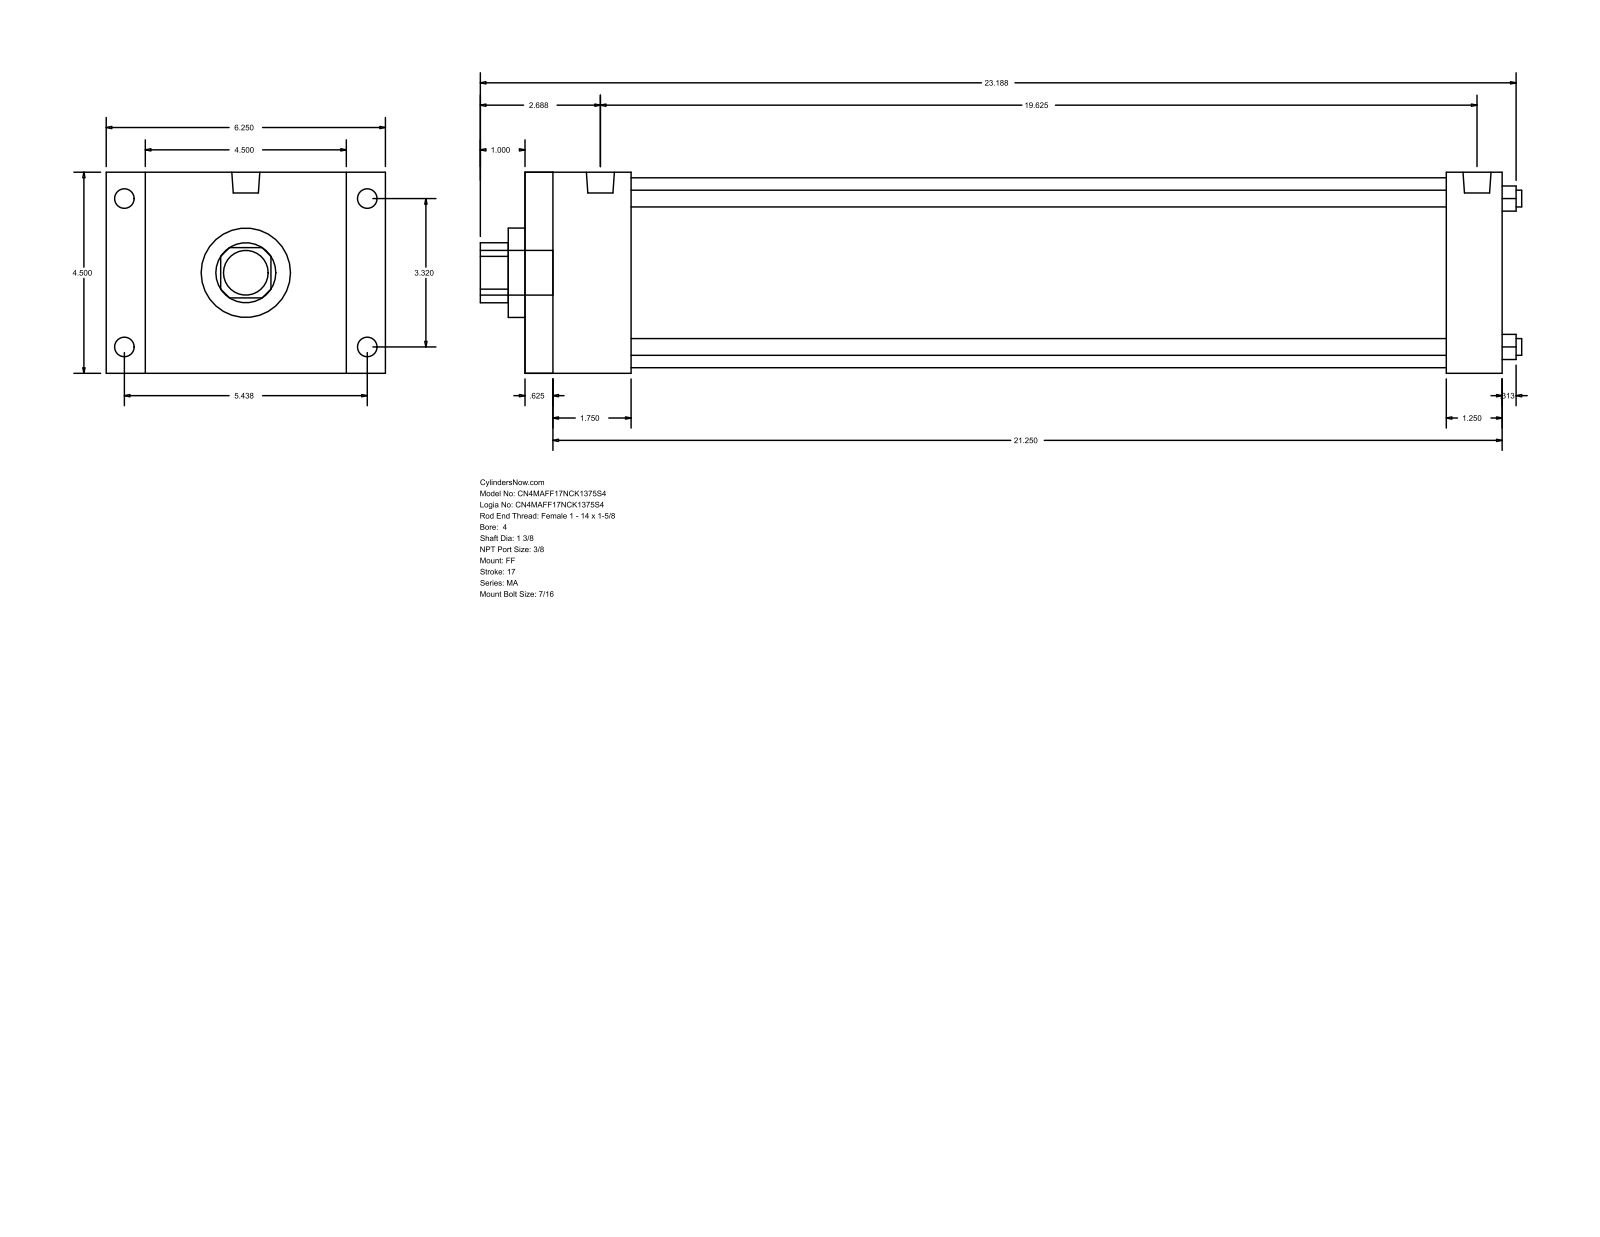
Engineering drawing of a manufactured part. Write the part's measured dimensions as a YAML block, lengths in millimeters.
part_name: "MA_FF__0400_1.375"
step_written_by: "GSSL Pune (CONFIG_CONTROL_DESIGN)"
units: millimeters
bodies: {solids: 0, faces: 92, planar: 64, cylindrical: 28, other: 0}
overall_size: [592.14, 158.75, 114.3]
round_holes:
  - {diameter: 9.53, count: 4}
  - {diameter: 34.92, count: 1}
  - {diameter: 50.8, count: 1}
  - {diameter: 107.95, count: 1}
round_bosses_or_shafts:
  - {diameter: 11.11, count: 8}
  - {diameter: 15.93, count: 2}
  - {diameter: 25.4, count: 1}
partial_cylinders:
  - {radius: 17.06, count: 1}
face_to_face_distances: [114.3, 555.62, 15.87, 539.75, 22.23, 136.53, 523.87, 508, 31.75, 60.32]
hole_center_spacings: [59.62, 84.32, 119.25]
